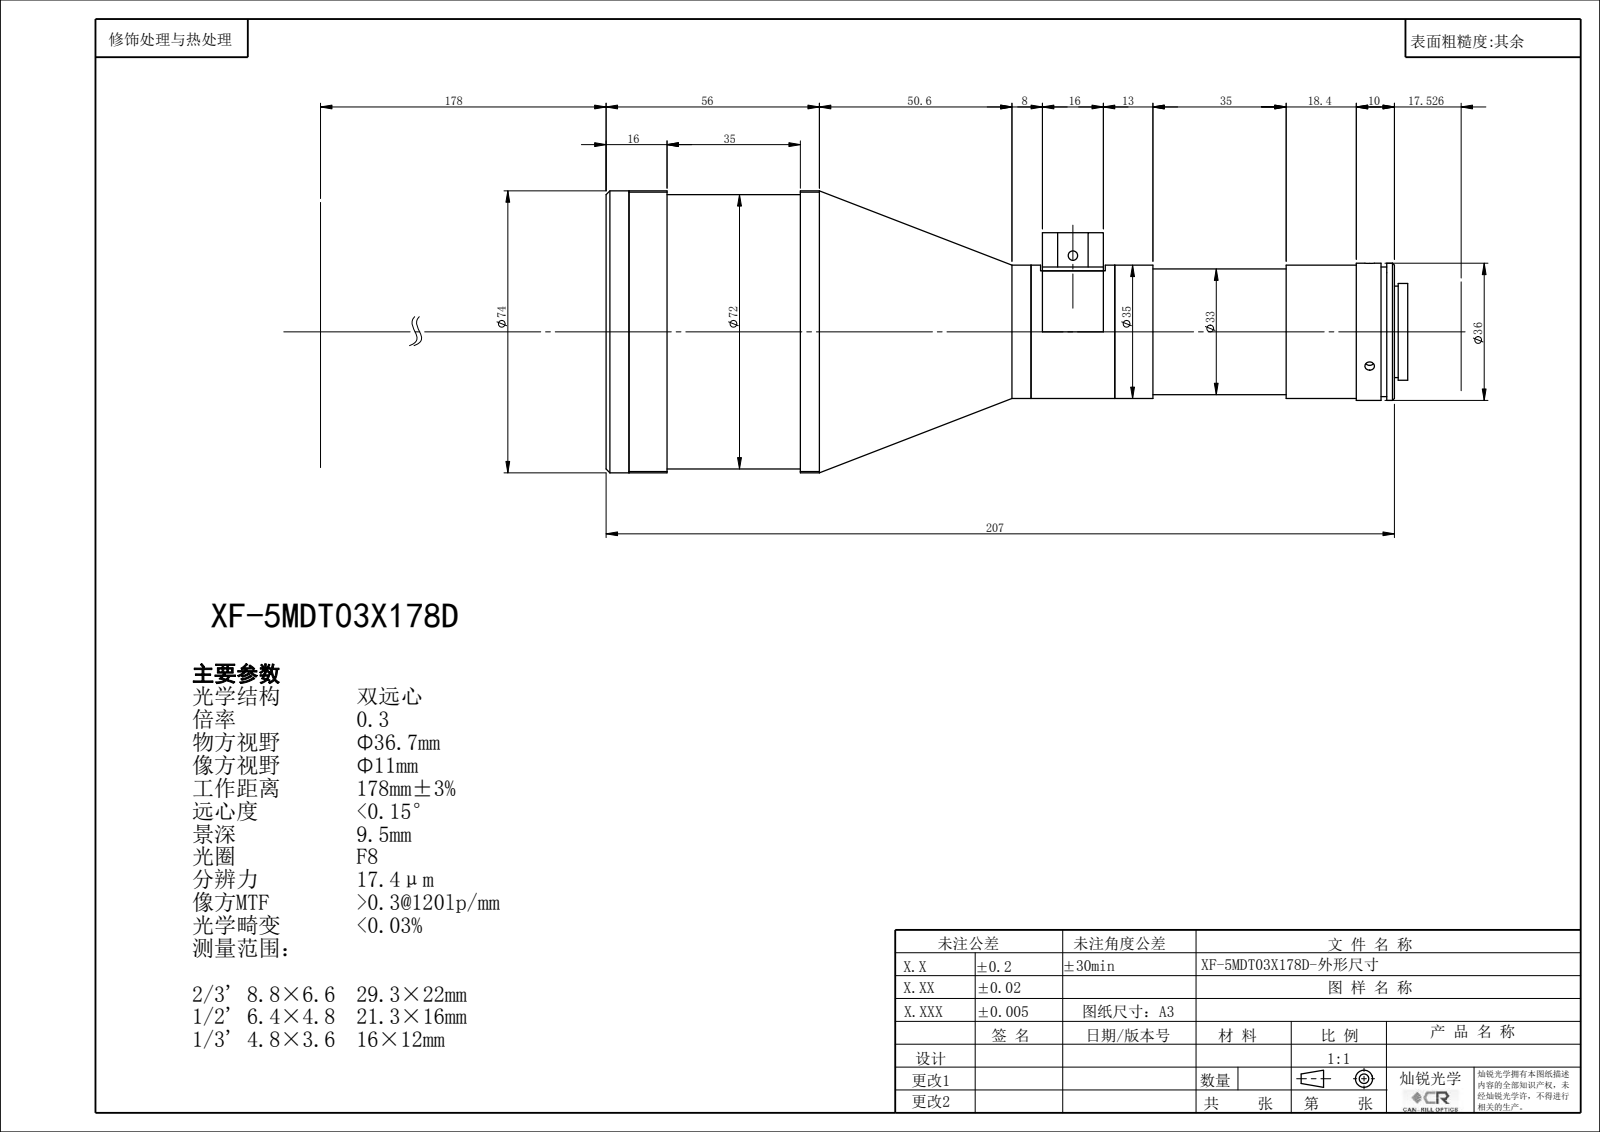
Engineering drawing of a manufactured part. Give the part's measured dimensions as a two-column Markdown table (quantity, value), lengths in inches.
| quantity | value |
| --- | --- |
| part name | XF-5MDT03X178D |
| STEP written by | SolidWorks 2014 (CONFIG_CONTROL_DESIGN) |
| units | inches |
| bodies | 0 solids, 129 faces (40 planar, 79 cylindrical, 10 other) |
| overall size | 8.287 × 2.913 × 2.913 |
| round holes (diameter × count) | 0.063 × 4, 0.087 × 4, 0.098 × 4, 0.551 × 1, 0.843 × 1, 0.945 × 1, 2.52 × 1, 2.638 × 1, 2.756 × 1 |
| round bosses / shafts (diameter × count) | 2.913 × 1, 2.835 × 1, 1.417 × 1, 1.378 × 1, 1.339 × 1, 1.299 × 1, 1 × 1 |
| partial cylindrical surfaces (radius × count) | 0.157 × 4 |
| main face-to-face distances | 0.394, 1.378, 0.236, 0.118, 0.748, 4.157, 4.393, 3.757, 7.913, 8.15 |
| hole center spacings | 0.629, 0.433, 1.181, 1.258, 2.912, 3.337, 3.068 |
